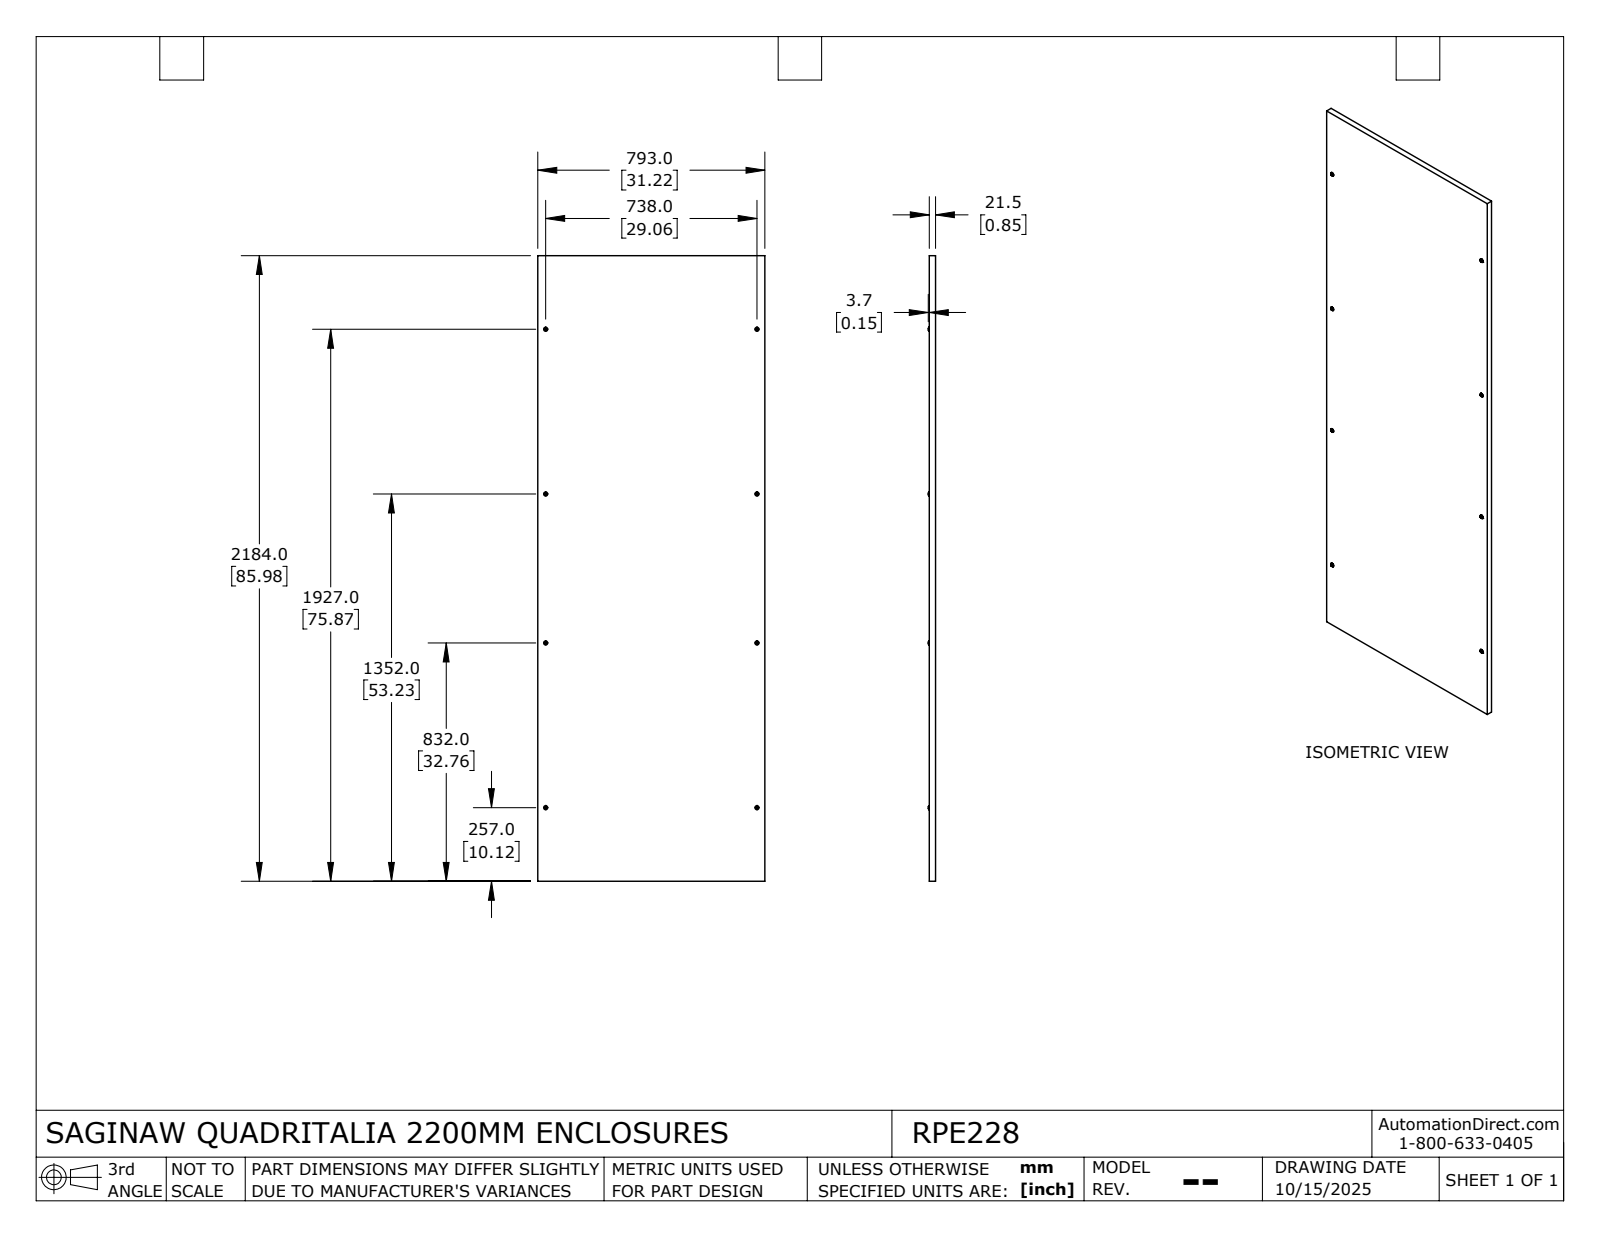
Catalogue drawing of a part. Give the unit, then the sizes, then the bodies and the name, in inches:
Units: inches
Overall size (bounding box): 85.984 × 31.22 × 0.992
Round holes (diameter × count): ⌀0.354 ×8
Round bosses / shafts (diameter × count): ⌀0.236 ×10, ⌀0.551 ×8, ⌀0.276 ×2
Partial cylindrical surfaces — rounded edges, fillets, slot ends (radius × count): R0.02 ×96, R0.296 ×4
Main face-to-face distances: 0.059, 31.161, 31.22, 31.102, 85.925, 85.984, 85.866, 0.846, 0.787, 0.63
Hole centre spacings: 22.638, 29.055, 36.833, 43.11, 51.987, 20.472, 35.543, 65.748
Volume: 197.6 in³ · Surface area: 5 824 in²
Bodies: 1 solid, 298 faces (144 planar, 128 cylindrical, 26 other)
Part name (STEP PRODUCT): RPE228
STEP written by: SolidWorks 2024 (AUTOMOTIVE_DESIGN)
